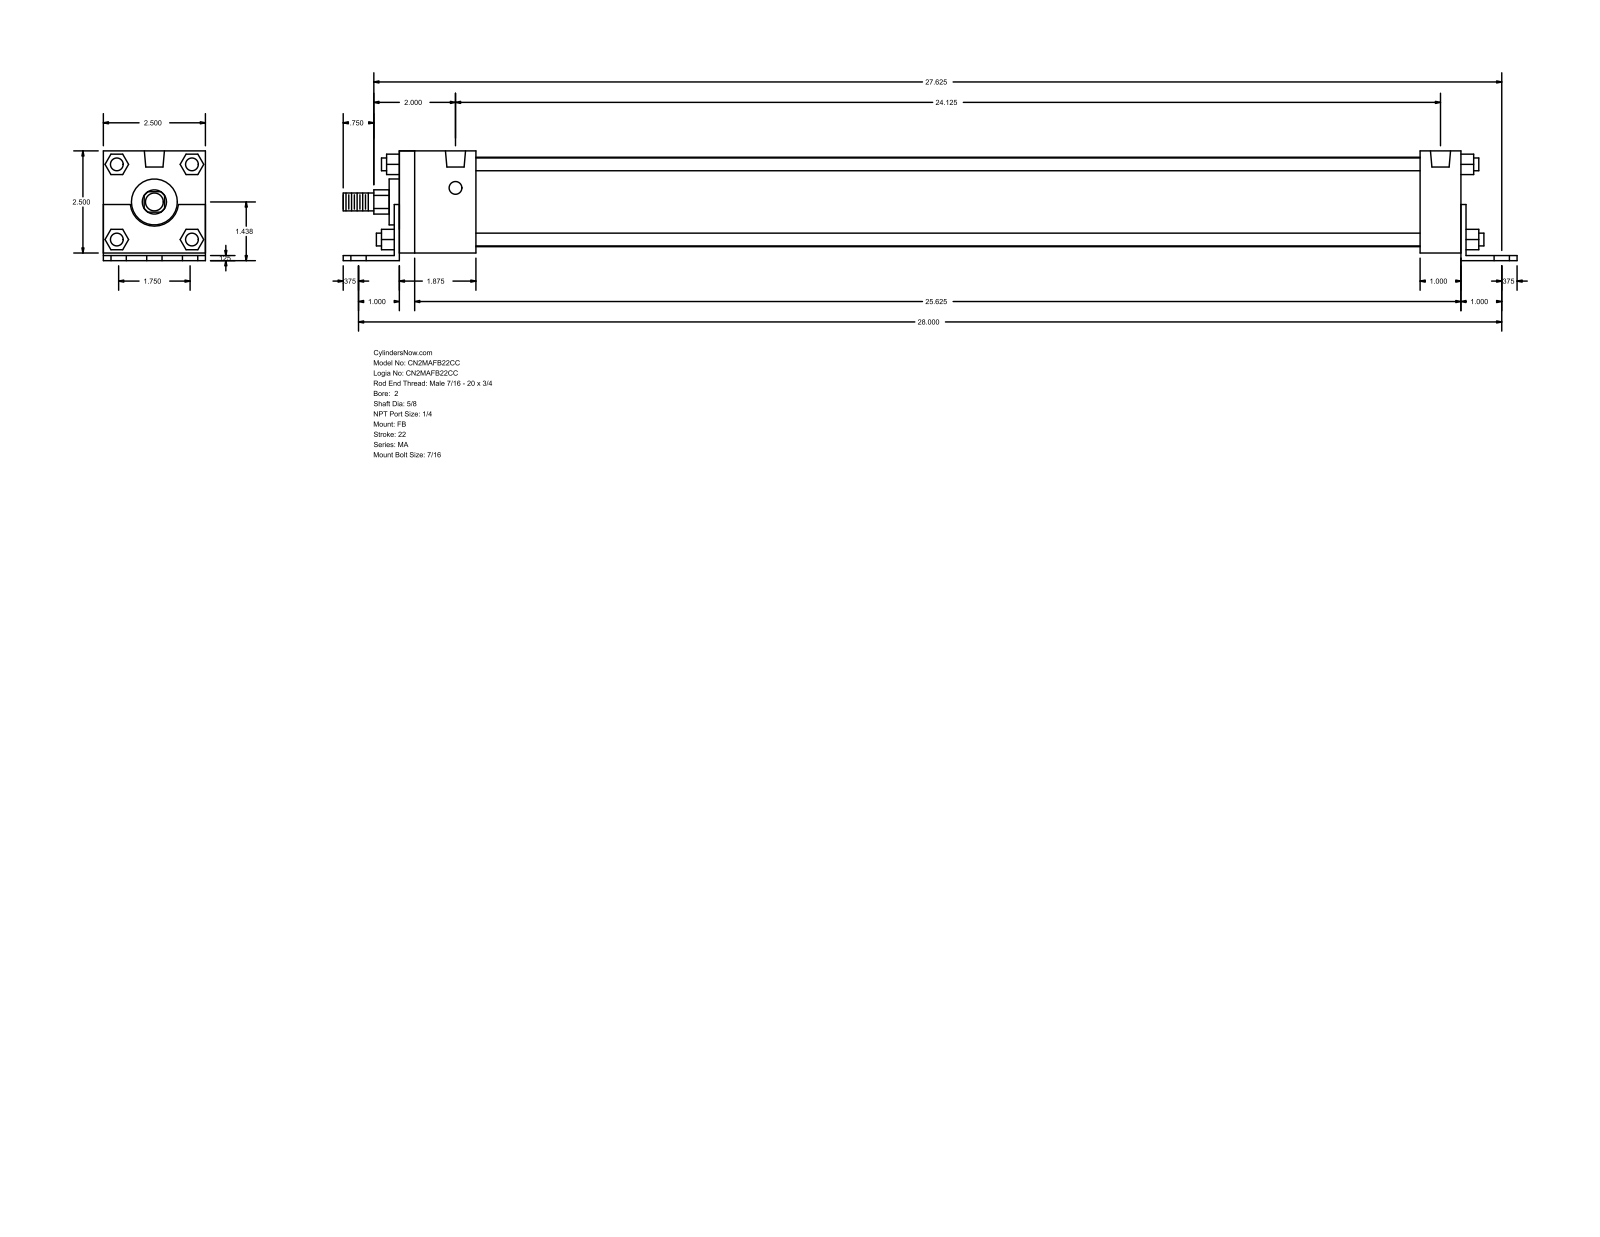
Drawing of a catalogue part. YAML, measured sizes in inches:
part_name: "MA_FB__0200_0.625"
step_written_by: "GSSL Pune (CONFIG_CONTROL_DESIGN)"
units: inches
bodies: {solids: 0, faces: 140, planar: 105, cylindrical: 35, other: 0}
overall_size: [28.75, 2.687, 2.5]
round_holes:
  - {diameter: 0.437, count: 6}
  - {diameter: 0.313, count: 4}
  - {diameter: 0.492, count: 2}
round_bosses_or_shafts:
  - {diameter: 0.313, count: 4}
  - {diameter: 2.19, count: 1}
  - {diameter: 1.125, count: 1}
  - {diameter: 0.625, count: 1}
  - {diameter: 0.437, count: 1}
partial_cylinders:
  - {radius: 0.297, count: 1}
  - {radius: 0.593, count: 1}
face_to_face_distances: [2.5, 0.187, 0.125, 2.687, 0.063, 0.125, 2.563, 26.125, 26, 0.5]
hole_center_spacings: [0.875, 28.014, 28, 1.736, 1.75, 2.531, 24.125, 25.64]
